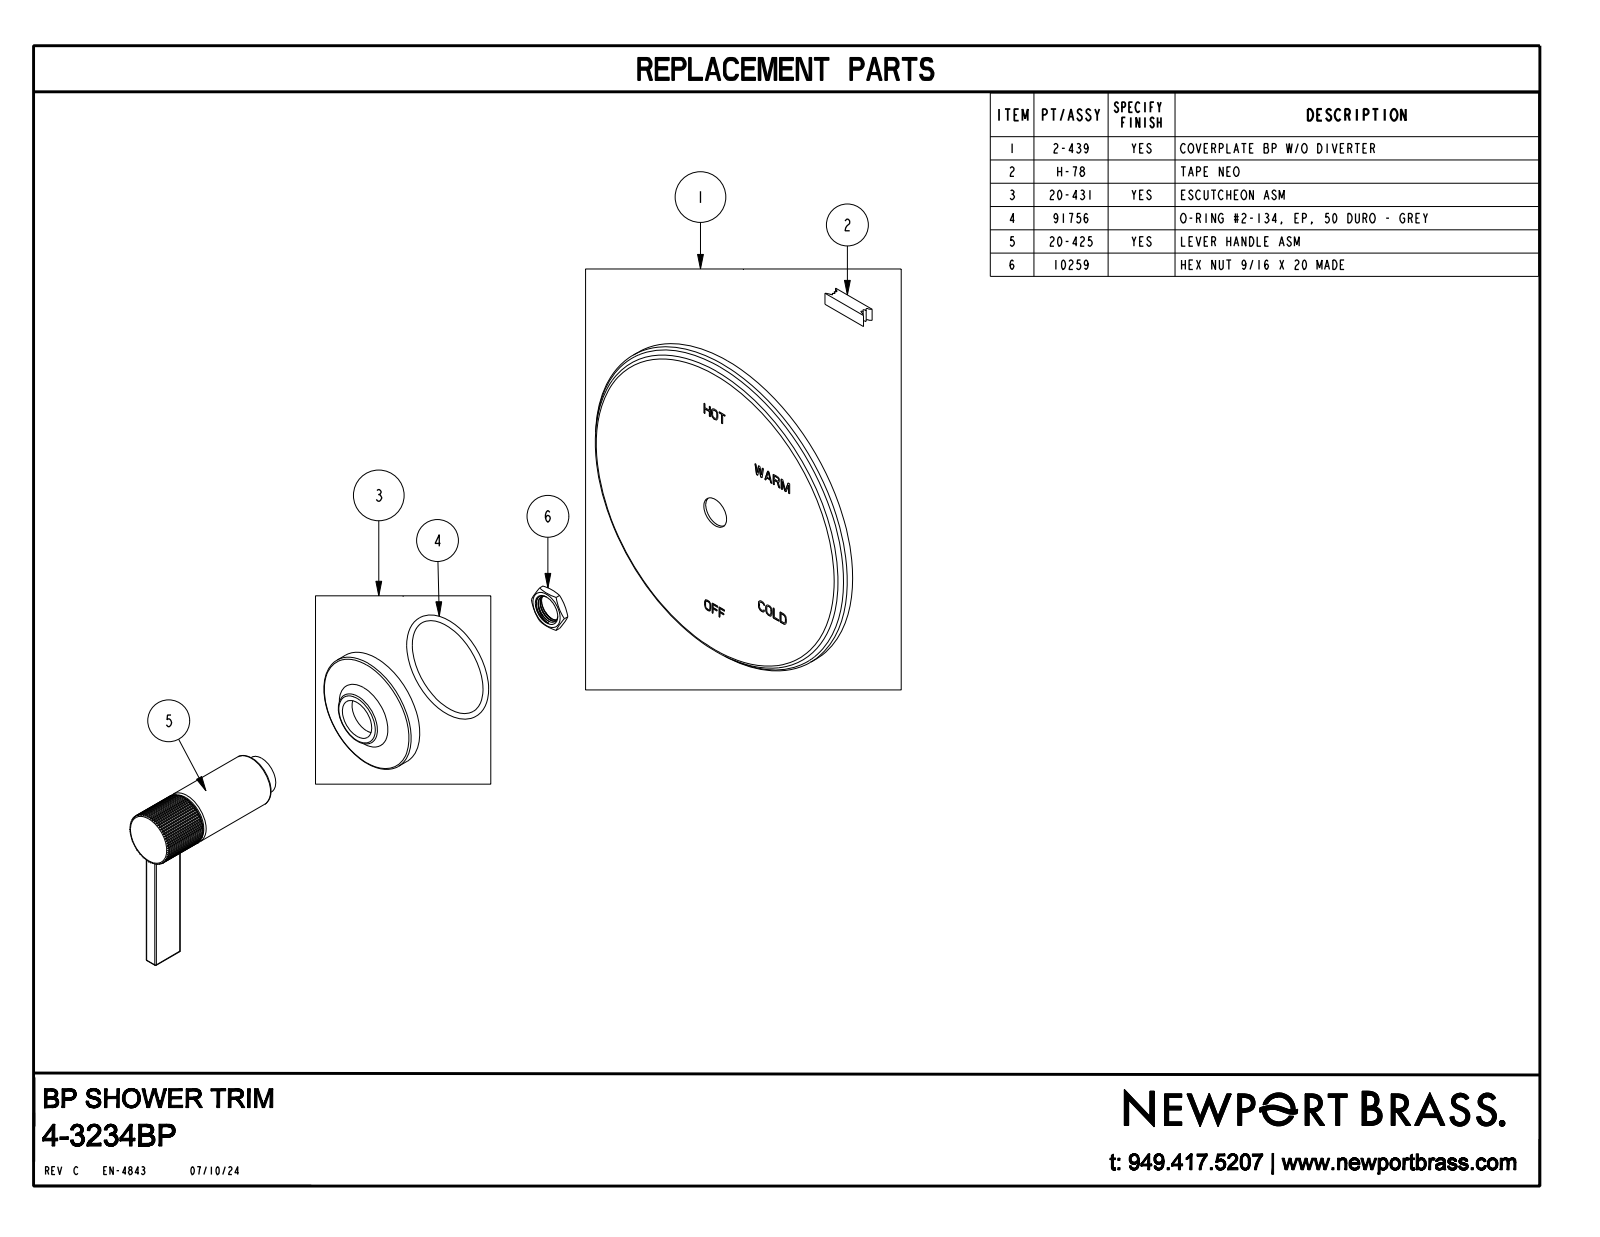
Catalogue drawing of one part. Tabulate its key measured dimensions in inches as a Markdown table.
| quantity | value |
| --- | --- |
| part name | 11117; H-78; 2-439_ASM; 13118 (+8 more) |
| STEP written by | CREO PARAMETRIC BY PTC INC, 2018400 (CONFIG_CONTROL_DESIGN) |
| units | inches |
| bodies | 16 solids, 1645 faces (859 planar, 526 cylindrical, 260 other) |
| overall size | 6.5 × 6.5 × 3.514 |
| volume | 4.923 in³ |
| surface area | 180.3 in² |
| round holes (diameter × count) | 0.11 × 2, 0.14 × 1, 0.15 × 1, 0.275 × 1, 0.335 × 1, 0.358 × 1, 0.375 × 1, 0.383 × 1, 0.397 × 1, 0.4 × 1, 0.42 × 1, 0.516 × 1 |
| round bosses / shafts (diameter × count) | 0.138 × 2, 6.5 × 1, 2.25 × 1, 1.812 × 1, 1 × 1, 0.85 × 1, 0.73 × 1, 0.572 × 1 |
| partial cylindrical surfaces (radius × count) | 0.02 × 12, 0.01 × 6, 0.042 × 6, 0.1 × 6, 0.03 × 4, 0.094 × 2, 0.072 × 1, 0.137 × 1 |
| main face-to-face distances | 0.05, 0.25, 0.225, 2.321, 0.624, 0.175, 3.251, 3.201, 3.026, 0.5 |
| hole center spacings | 0.335 |
